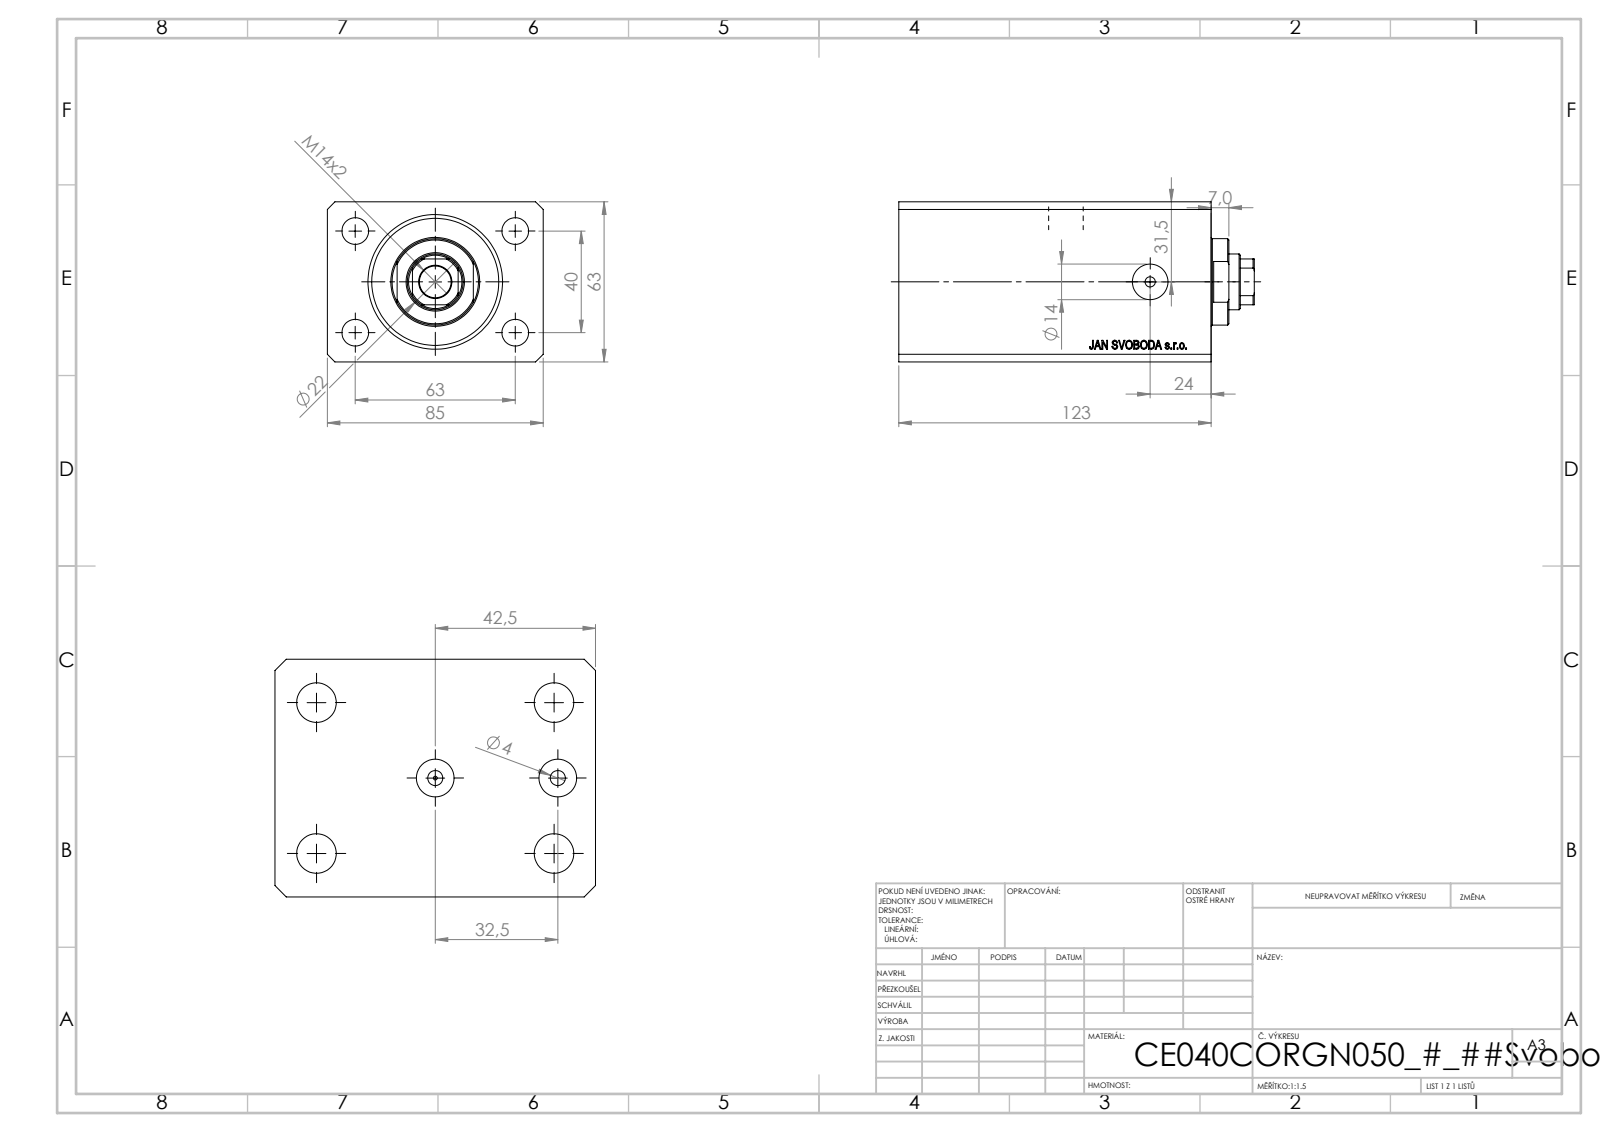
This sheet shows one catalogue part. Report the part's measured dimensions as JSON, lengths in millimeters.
{"part_name": "V250CE_VC_C; V250CE_C_VCP; V250CE_C_Body", "step_written_by": "SolidWorks 2019 (CONFIG_CONTROL_DESIGN)", "units": "millimeters", "bodies": {"solids": 3, "faces": 868, "planar": 428, "cylindrical": 46, "other": 394}, "overall_size": [140, 85, 63], "volume_mm3": 572992, "surface_area_mm2": 102621, "round_holes": [[4, 4], [10.5, 4], [10, 2], [14, 2], [1.25, 1], [12.5, 1], [22, 1], [40, 1], [53, 1]], "round_bosses_or_shafts": [[34, 1]], "partial_cylinders_radius": [[10.5, 1]], "face_to_face_distances": [63, 85, 123, 17, 106, 11.4, 94.6, 111.6, 100.4, 56], "hole_center_spacings": [37.31, 20.02, 40, 63, 67.05, 74.63, 32.5, 75]}
